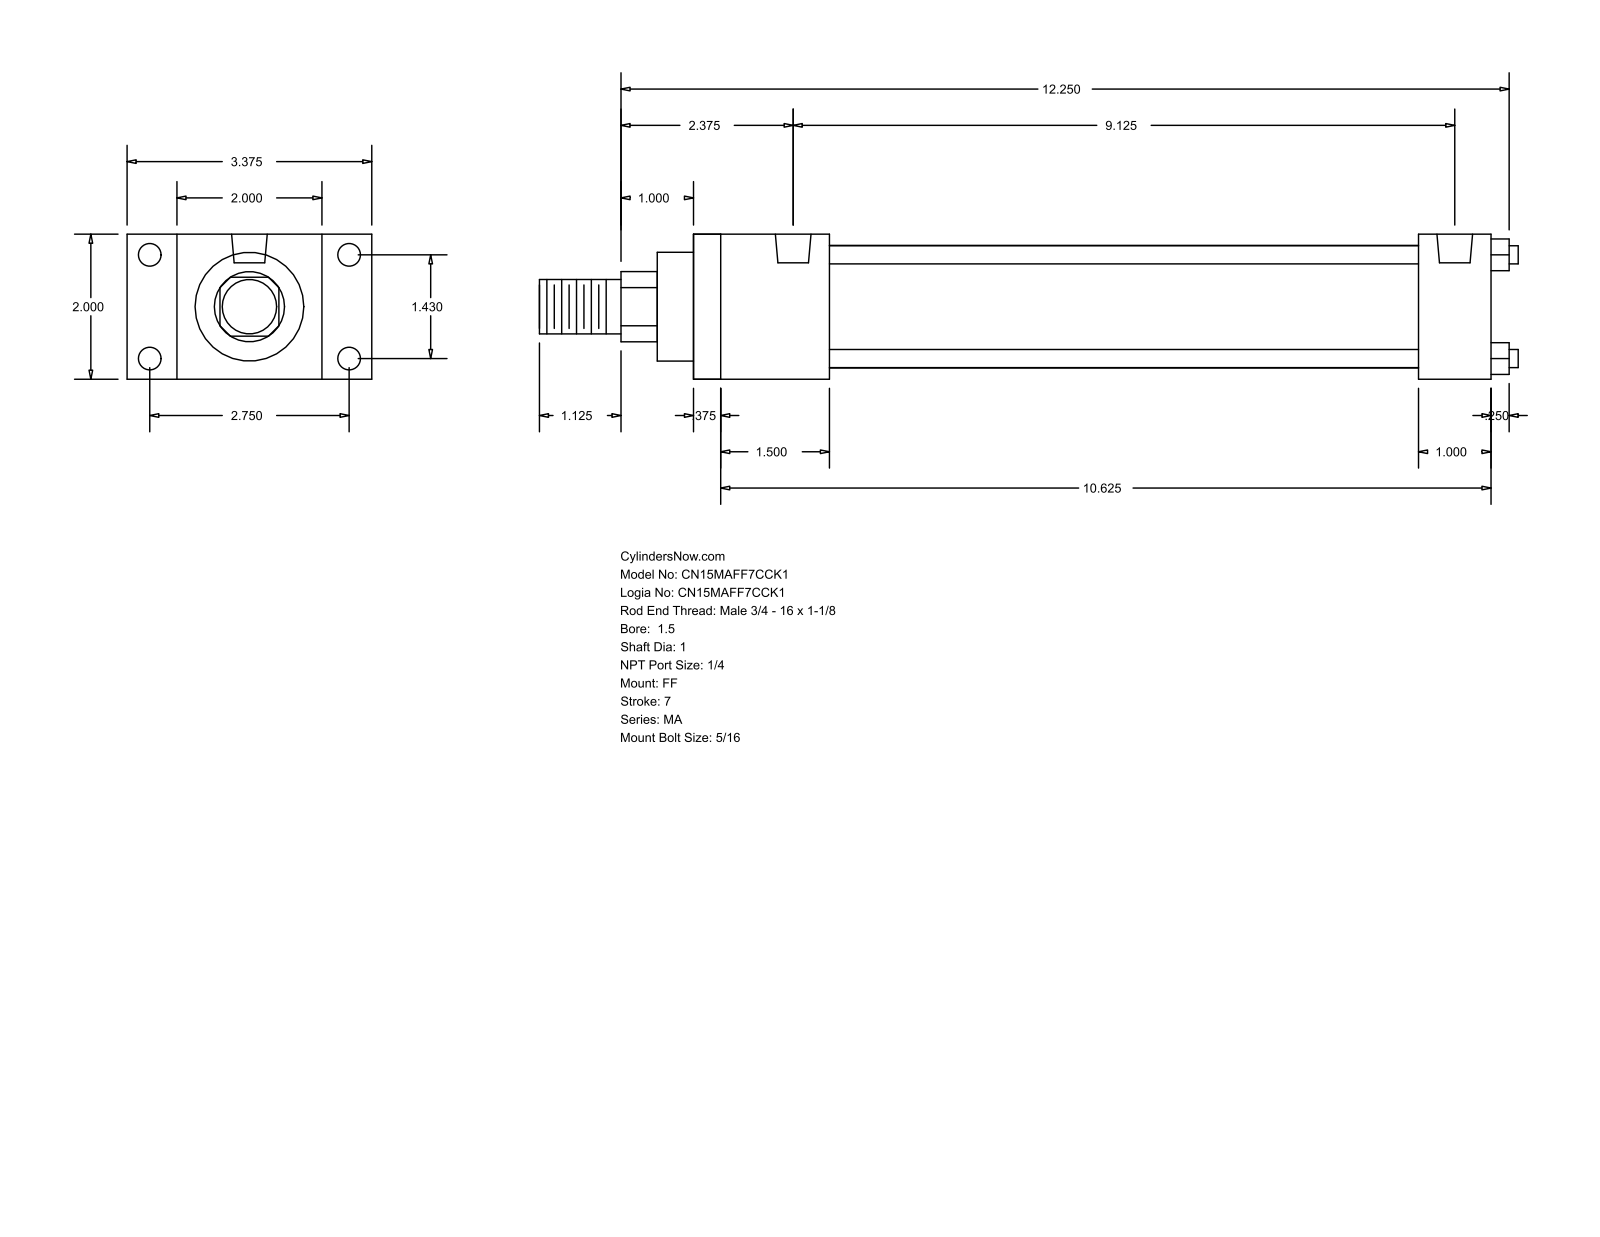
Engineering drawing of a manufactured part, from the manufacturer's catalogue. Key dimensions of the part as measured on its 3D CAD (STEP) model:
Part name (STEP PRODUCT): MA_FF__0150_1
STEP written by: GSSL Pune (CONFIG_CONTROL_DESIGN)
Units: millimetres
Bodies: 0 solids, 92 faces (64 planar, 28 cylindrical, 0 other)
Overall size (bounding box): 342.9 × 85.72 × 50.8
Round holes (diameter × count): ⌀7.94 ×8, ⌀12.49 ×2
Round bosses / shafts (diameter × count): ⌀6.35 ×4, ⌀42.93 ×1, ⌀38.1 ×1, ⌀25.4 ×1, ⌀19.05 ×1
Partial cylindrical surfaces — rounded edges, fillets, slot ends (radius × count): R12.29 ×1
Main face-to-face distances: 50.8, 279.4, 9.52, 269.88, 25.4, 47.63, 254, 38.11, 244.48, 206.37
Hole centre spacings: 36.32, 69.84, 78.72, 231.77
